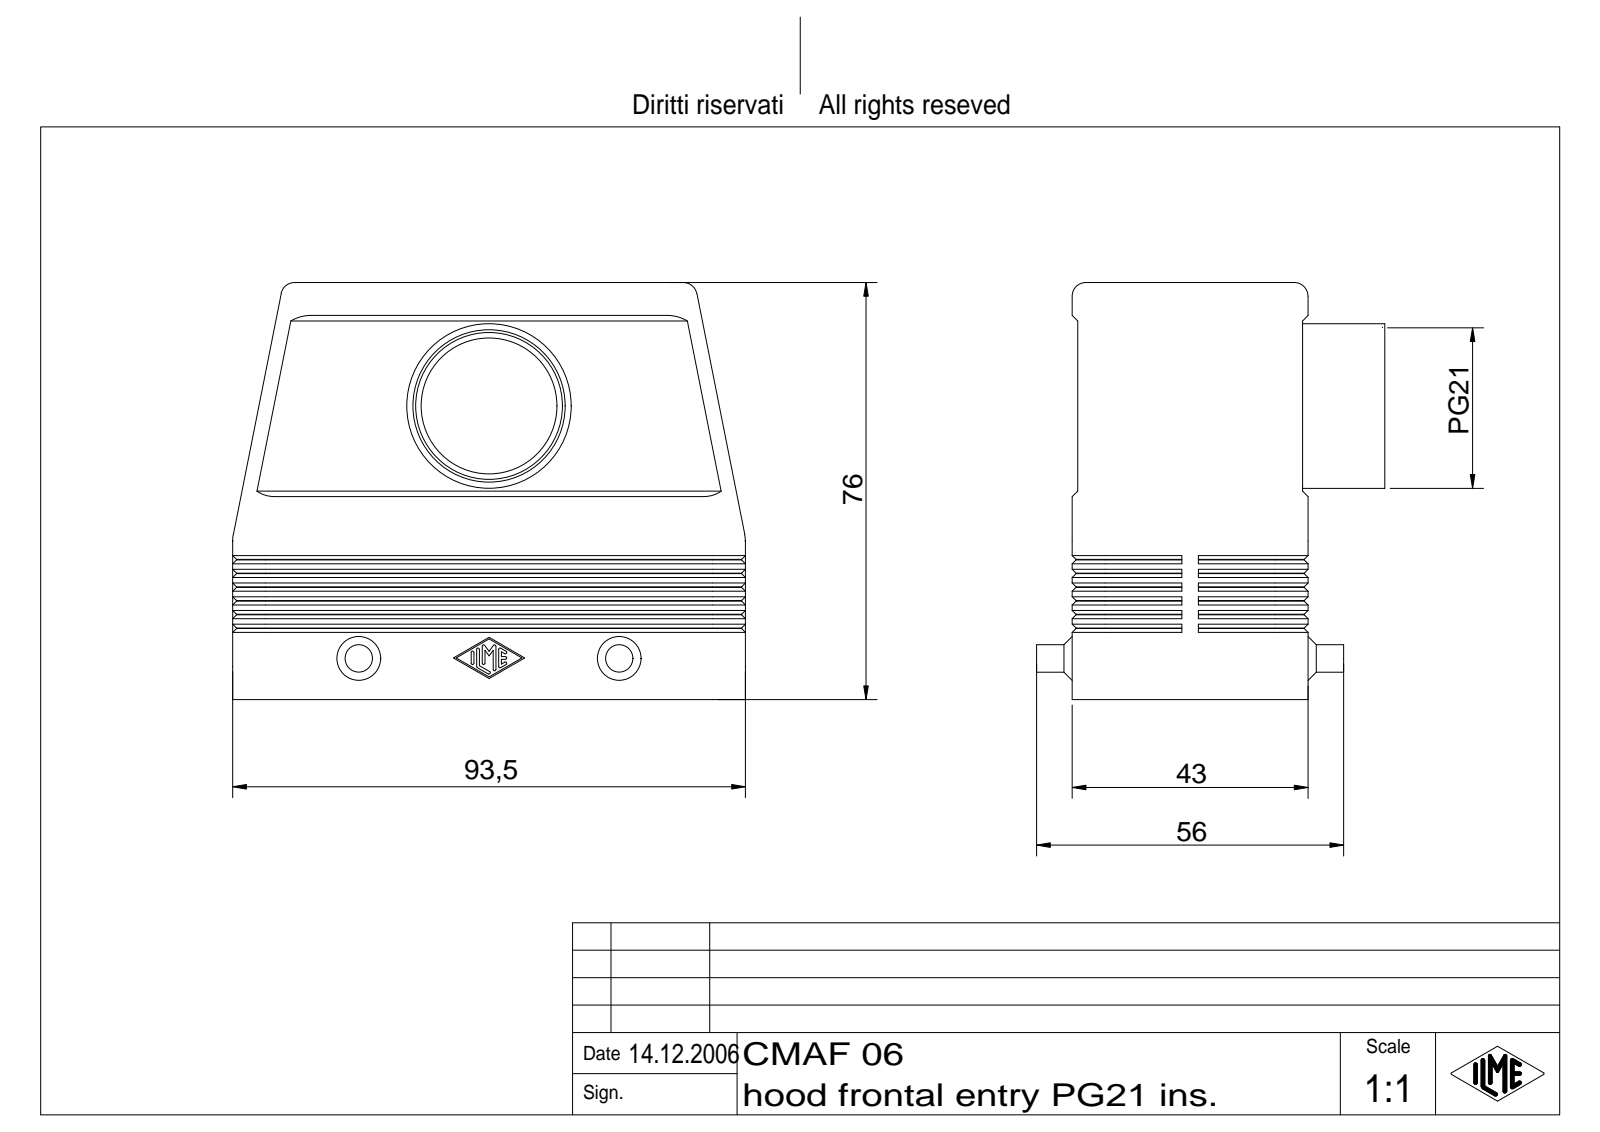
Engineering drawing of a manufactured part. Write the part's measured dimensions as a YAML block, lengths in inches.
part_name: "CAO Tüllengehäuse 2 Bügel für einen Einsatz"
step_written_by: "Autodesk Inventor 7 (AUTOMOTIVE_DESIGN)"
units: inches
bodies: {solids: 1, faces: 417, planar: 159, cylindrical: 110, other: 148}
overall_size: [2.874, 2.756, 2.421]
volume: 3.666
surface_area: 55.4
round_holes:
  - {diameter: 0.754, count: 1}
  - {diameter: 0.833, count: 1}
round_bosses_or_shafts:
  - {diameter: 0.197, count: 2}
  - {diameter: 0.945, count: 1}
partial_cylinders:
  - {radius: 0.01, count: 14}
  - {radius: 0.236, count: 10}
  - {radius: 0.079, count: 4}
  - {radius: 0.098, count: 4}
  - {radius: 0.118, count: 4}
  - {radius: 0.209, count: 2}
  - {radius: 0.787, count: 1}
face_to_face_distances: [0.118, 0.079, 1.575, 1.535, 0.039, 1.654, 1.457, 0.354, 0.472, 0.197]
